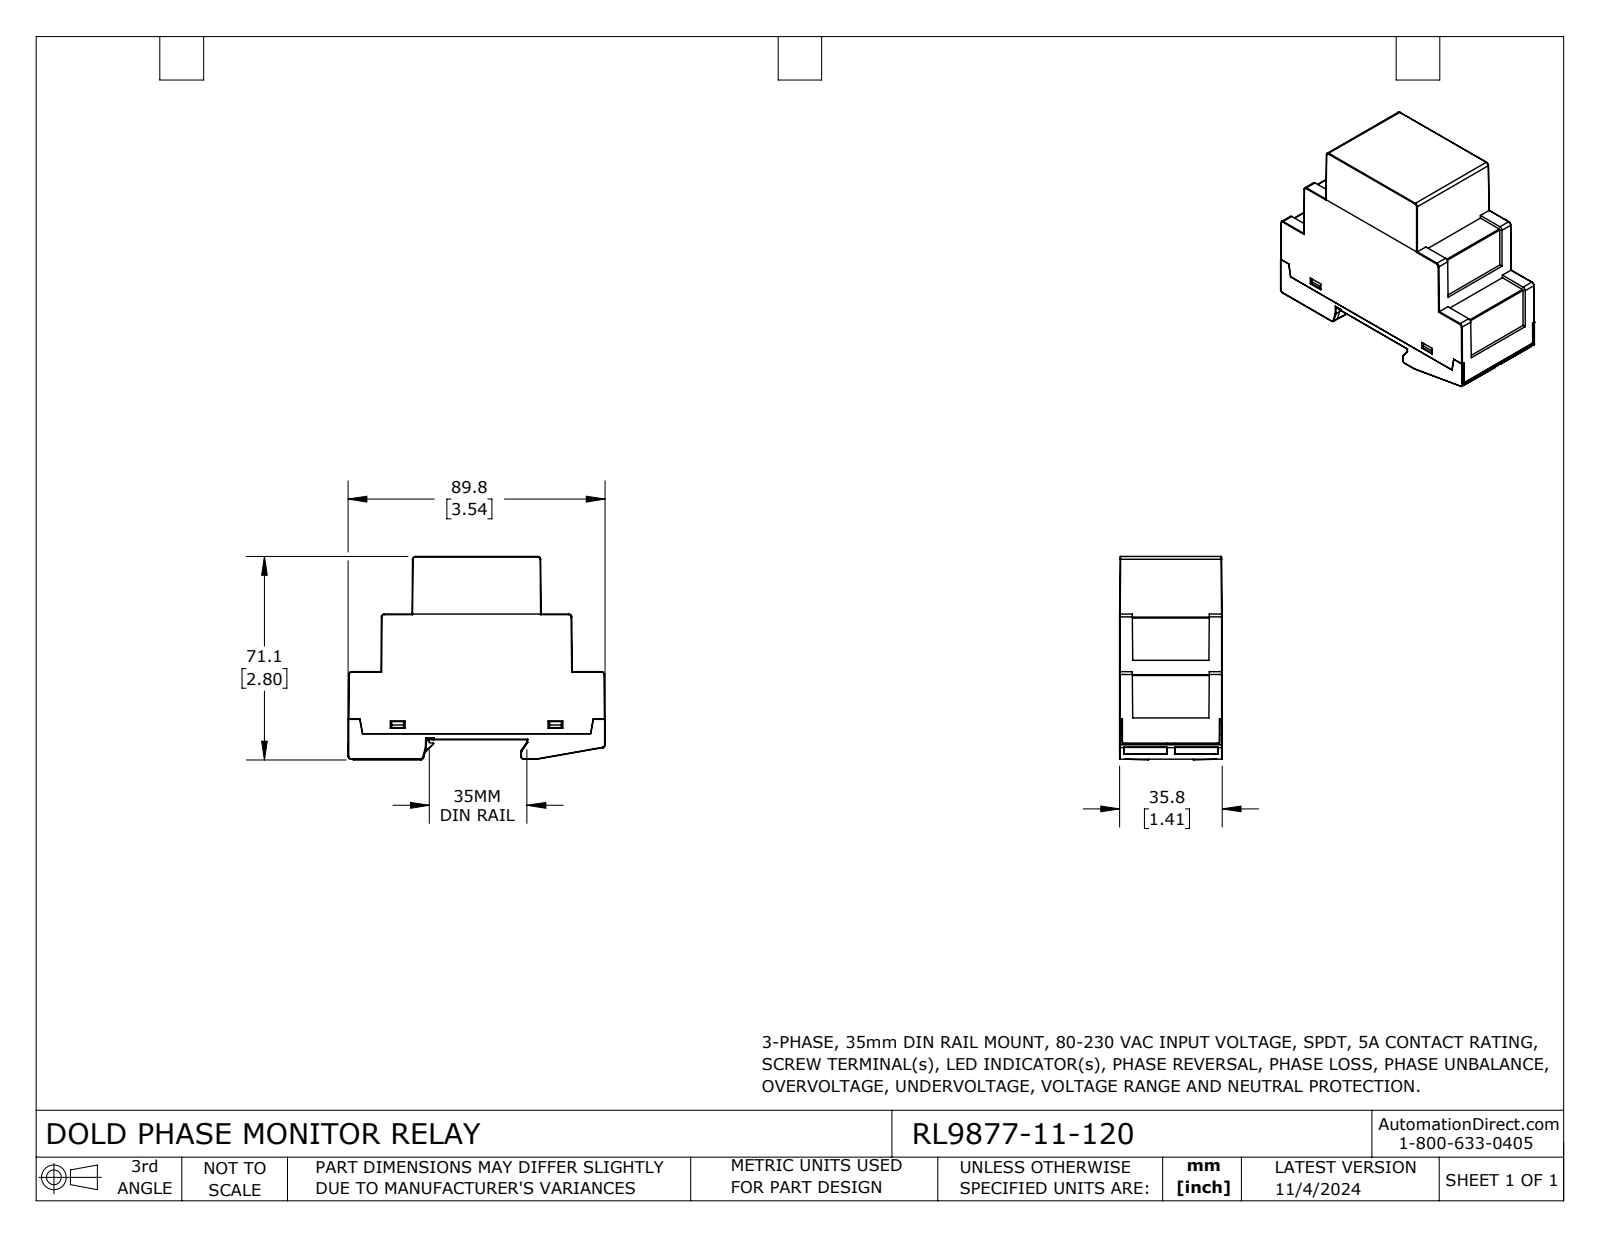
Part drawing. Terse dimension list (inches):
name: RL9877-11-120
written by: SolidWorks 2023 (CONFIG_CONTROL_DESIGN)
unit: in
bodies: 2 solids, 631 faces (484 planar, 109 cylindrical, 38 other)
size: 3.538 × 2.799 × 1.409
volume: 9.341 in³; area: 55.26 in²
bosses: 2× ⌀0.098, 1× ⌀0.315
rounds: 42× R0.008, 14× R0.039, 11× R0.02, 6× R0.004, 4× R0.012, 1× R0.011, 1× R0.016, 1× R0.028
face distances: 1.409, 0.217, 2.52, 0.035, 0.085, 2.435, 2.219, 0.301, 0.824, 1.374
